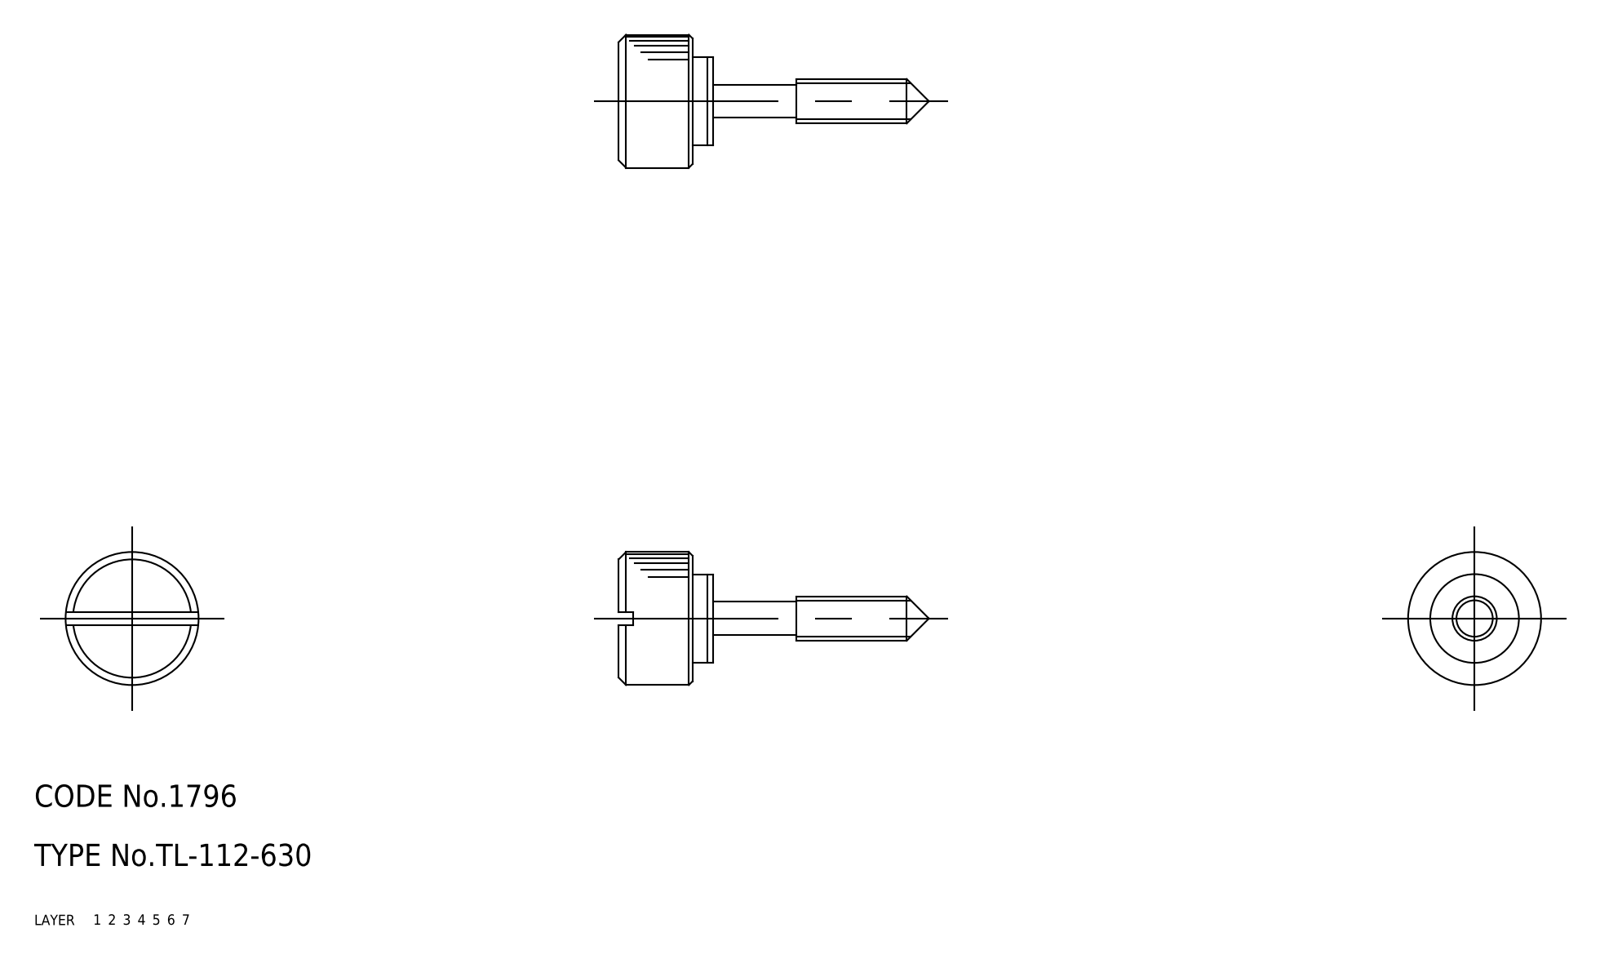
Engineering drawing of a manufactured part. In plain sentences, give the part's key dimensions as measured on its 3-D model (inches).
The part is named "washer; knob; TL_112_630_8958_36". Its 3-D file was written by "CADfix (AUTOMOTIVE_DESIGN)". It is 2 solids with 42 faces: 0 planar, 0 cylindrical and 42 other. Overall it measures 1.654 by 0.709 by 0.709 inches. Its volume is 0.207 cubic inches and its surface area 2.902 square inches.
